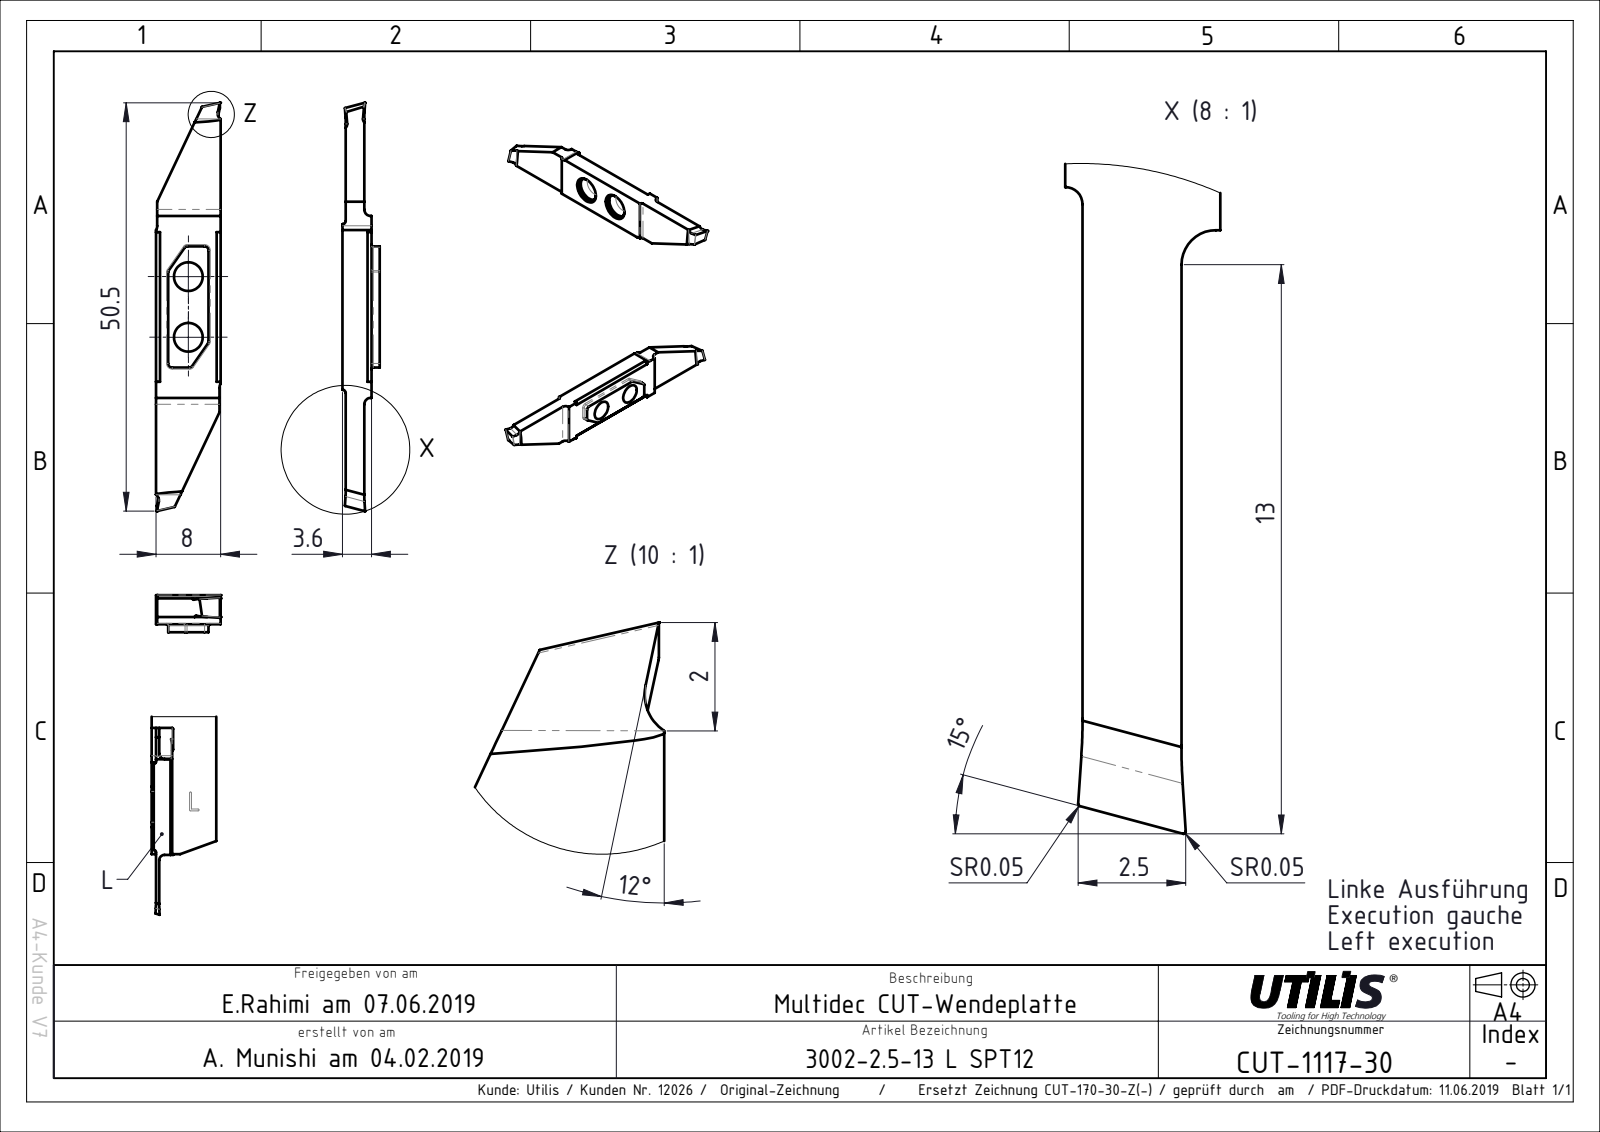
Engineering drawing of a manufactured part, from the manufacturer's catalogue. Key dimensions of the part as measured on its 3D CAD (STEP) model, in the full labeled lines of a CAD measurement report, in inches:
Part name (STEP PRODUCT): CUT-1117; ASME Y14.5
STEP written by: FormatWorks Professional (AP242_MANAGED_MODEL_BASED_3D_ENGINEERING_MIM_LF)
Units: inches
Bodies: 1 solid, 44 faces (28 planar, 16 cylindrical, 0 other)
Overall size (bounding box): 1.988 × 0.315 × 0.142
Volume: 0.055 in³ · Surface area: 1.553 in²
Round holes (diameter × count): ⌀0.14 ×2
Partial cylindrical surfaces — rounded edges, fillets, slot ends (radius × count): R0.016 ×2, R0.031 ×2, R0.039 ×2
Main face-to-face distances: 0.016, 0.142, 0.126, 0.106, 0.091, 0.035, 0.315, 0.712, 0.309, 0.303
Hole centre spacings: 0.295
